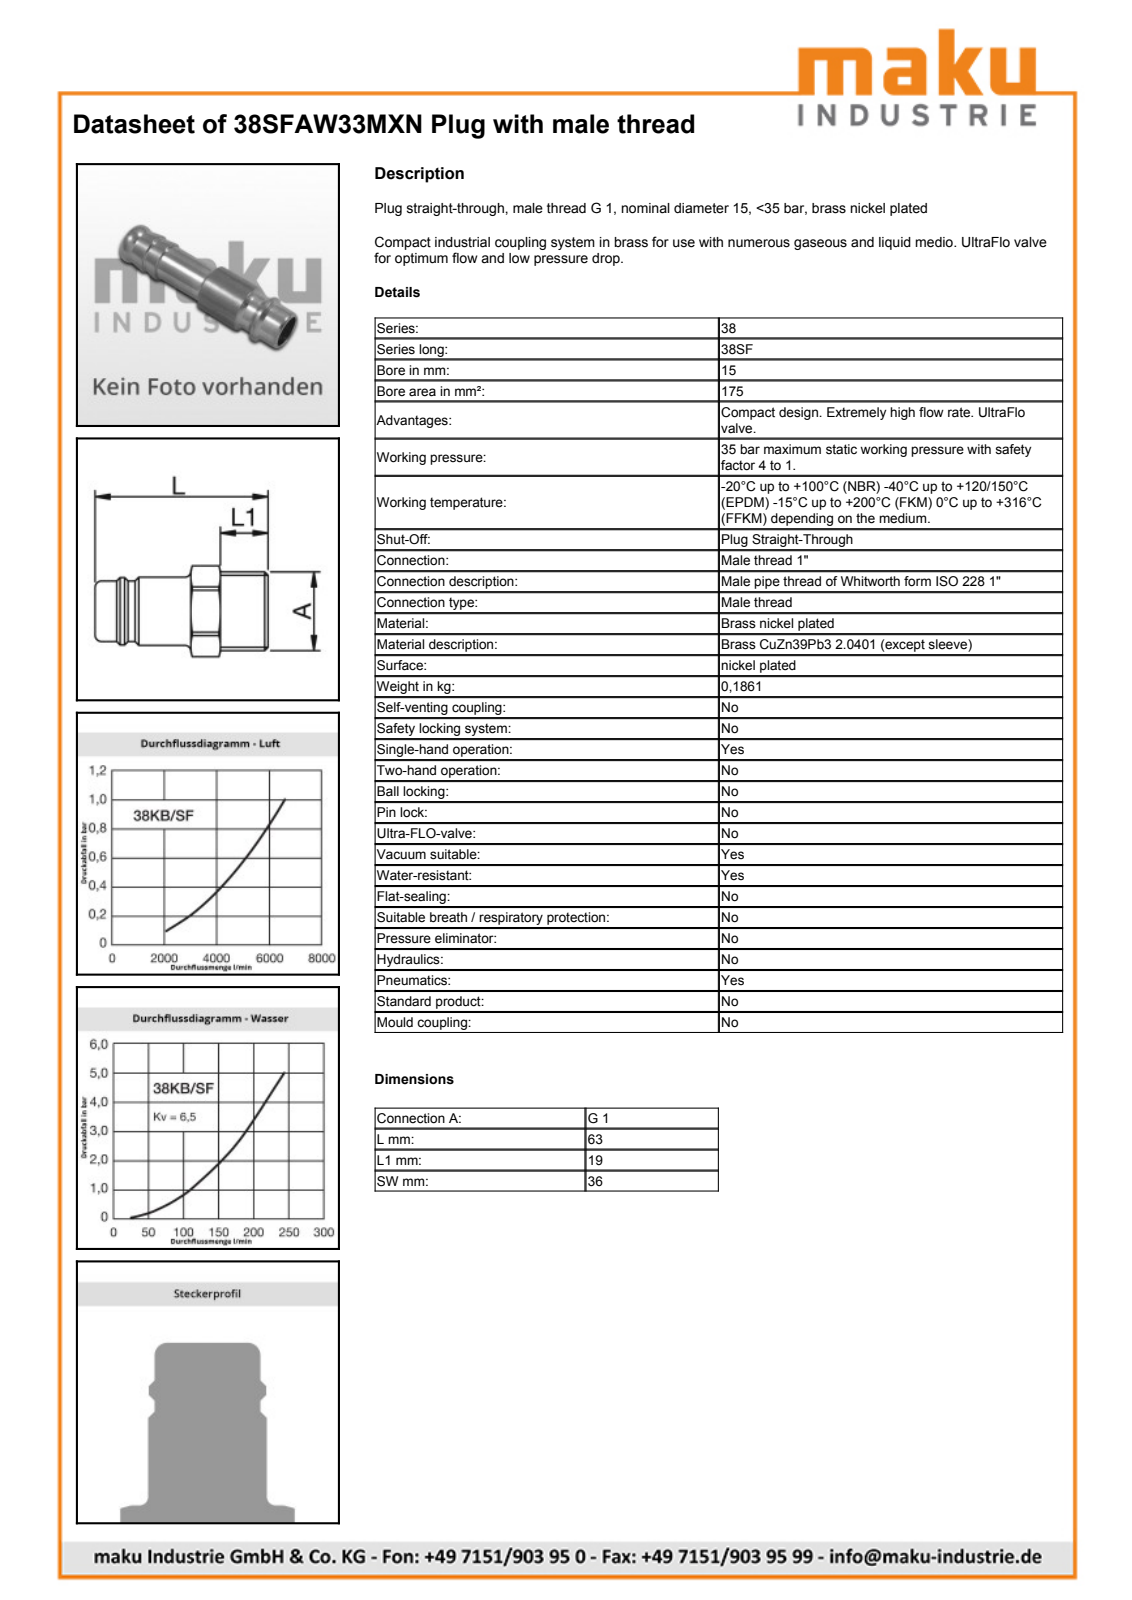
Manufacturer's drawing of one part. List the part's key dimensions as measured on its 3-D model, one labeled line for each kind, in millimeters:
Part name (STEP PRODUCT): D111275
STEP written by: Autodesk Inventor 2013 (AUTOMOTIVE_DESIGN)
Units: millimetres
Bodies: 1 solid, 42 faces (10 planar, 13 cylindrical, 19 other)
Overall size (bounding box): 63 × 40.35 × 36
Volume: 23 448 mm³ · Surface area: 10 879 mm²
Round holes (diameter × count): ⌀15 ×1, ⌀24 ×1
Round bosses / shafts (diameter × count): ⌀33.25 ×1, ⌀22.85 ×1, ⌀22.6 ×1, ⌀20.3 ×1
Partial cylindrical surfaces — rounded edges, fillets, slot ends (radius × count): R20.18 ×1
Main face-to-face distances: 36, 30.9, 11.9, 19, 32.1, 44, 63
